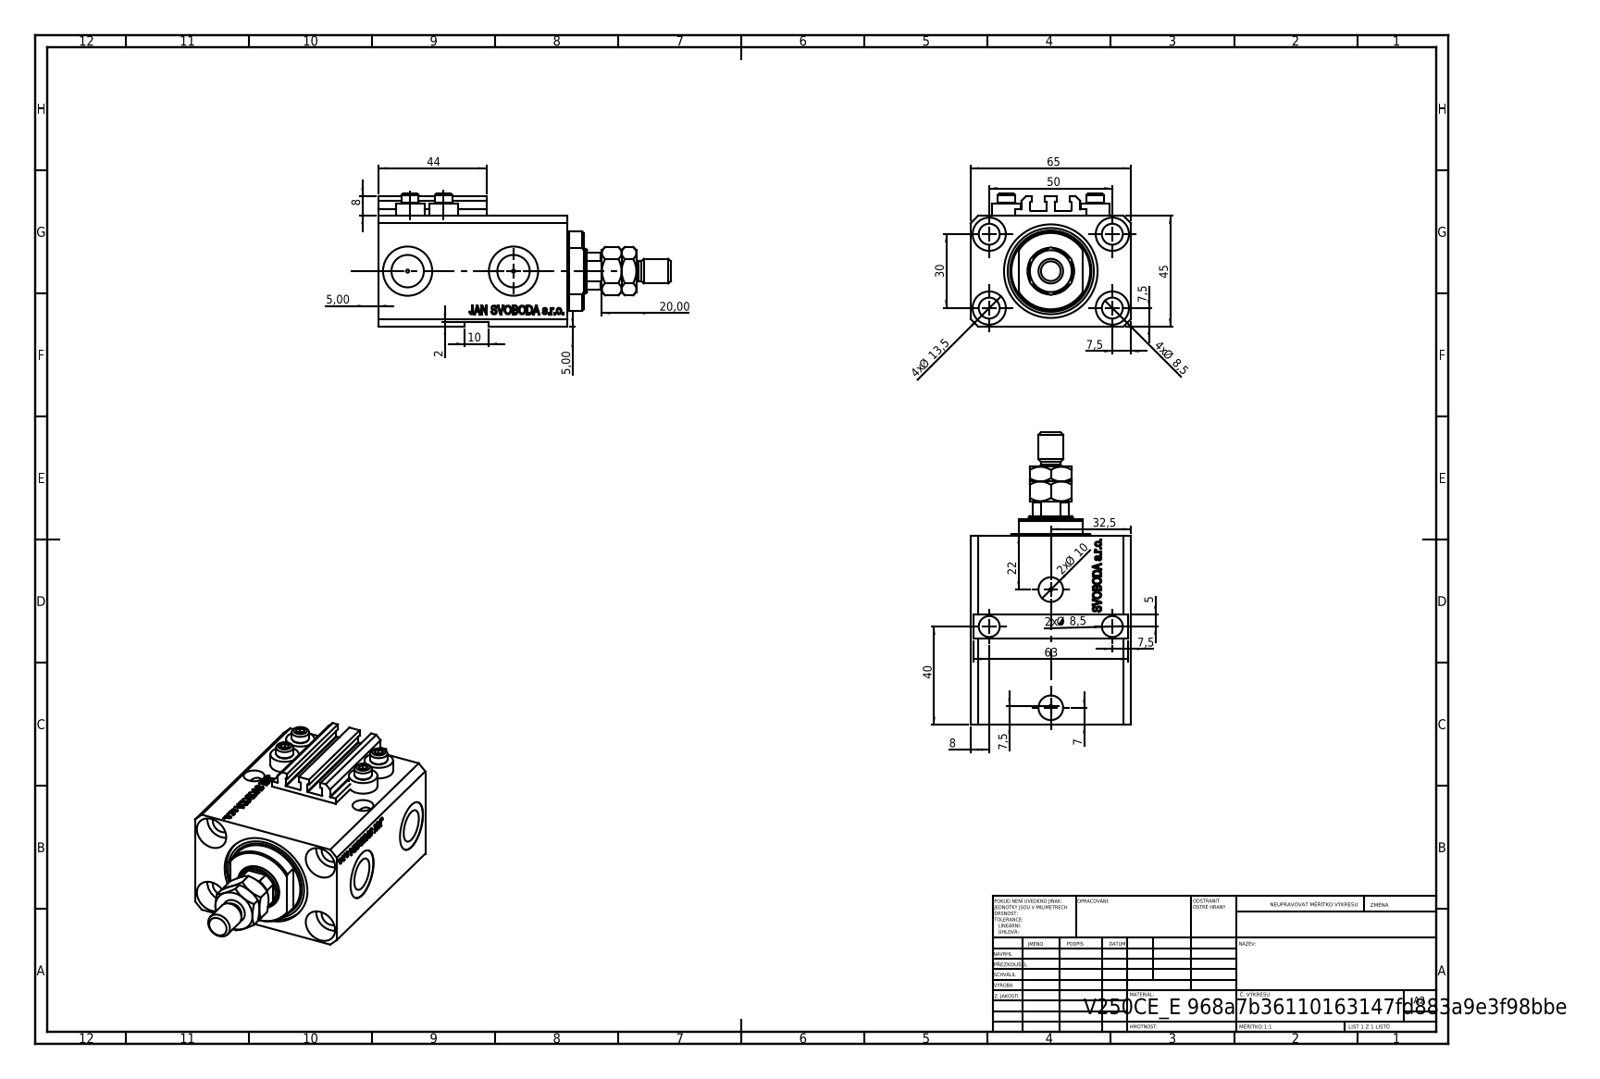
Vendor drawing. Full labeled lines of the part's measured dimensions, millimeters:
Part name (STEP PRODUCT): V250CE_C_VCP; MTA; V250CE_E_Body; V250CE_VC_E (+1 more)
STEP written by: SolidWorks 2019 (CONFIG_CONTROL_DESIGN)
Units: millimetres
Bodies: 9 solids, 1132 faces (530 planar, 142 cylindrical, 460 other)
Overall size (bounding box): 118.9 × 65 × 54
Volume: 200 643 mm³ · Surface area: 64 140 mm²
Round holes (diameter × count): ⌀8.5 ×7, ⌀1.25 ×4, ⌀4 ×4, ⌀13.5 ×4, ⌀10 ×2, ⌀13.16 ×2, ⌀20 ×2, ⌀18 ×1, ⌀25 ×1, ⌀38 ×1
Round bosses / shafts (diameter × count): ⌀11.6 ×4, ⌀7 ×4, ⌀10 ×1, ⌀8 ×1
Partial cylindrical surfaces — rounded edges, fillets, slot ends (radius × count): R0.2 ×10, R8.5 ×1, R16 ×1
Main face-to-face distances: 45, 65, 51.9, 6.9, 77, 25.1, 2, 70.1, 3, 9
Hole centre spacings: 29.15, 50, 13.6, 15.12, 18.81, 18.97, 26.22, 26.61
